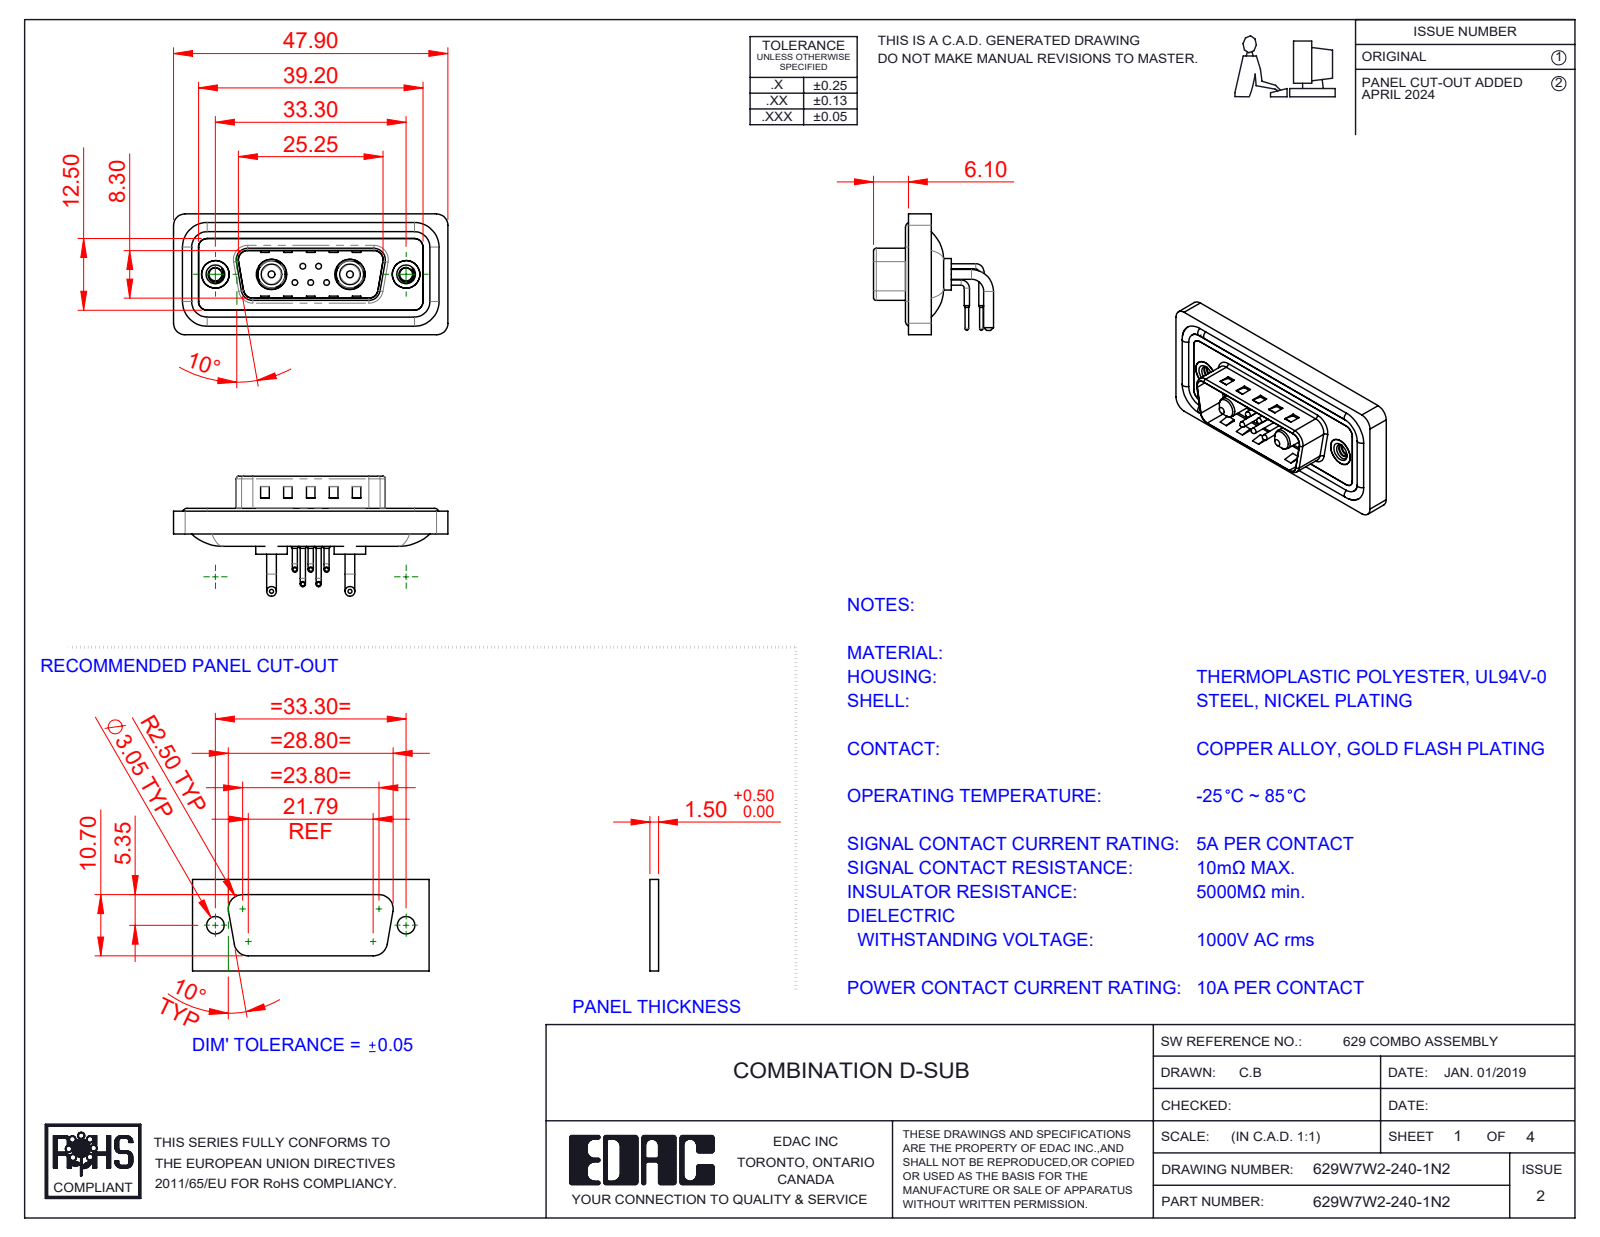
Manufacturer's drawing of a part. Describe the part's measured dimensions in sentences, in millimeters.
The part is named "629Combo Contact Row 1; 629W7W2-140-1N2; 629Combo Housing_7W2; 629Combo Threaded Rivet_2 (+5 more)". Its 3-D file was written by "SolidWorks 2023 (CONFIG_CONTROL_DESIGN)". It is 16 solids with 1083 faces: 517 planar, 406 cylindrical and 160 other. Overall it measures 47.9 by 21.1 by 20.95 millimeters. Its volume is 5 575 cubic millimeters and its surface area 9 039 square millimeters. Round holes: 5 of diameter 0.75, 5 of diameter 1.6, 5 of diameter 2, 2 of diameter 2.26, 2 of diameter 4, 2 of diameter 4.8, 2 of diameter 4.85, 2 of diameter 5, 2 of diameter 5.3. Round bosses or shafts: 10 of diameter 0.9, 5 of diameter 1.5, 5 of diameter 1, 5 of diameter 0.65, 4 of diameter 1.7, 4 of diameter 1.6, 2 of diameter 5.5, 2 of diameter 5.2. Partial cylindrical surfaces (rounded edges, fillets, slot ends): 20 of radius 2, 18 of radius 1.5, 8 of radius 0.5, 8 of radius 1.6, 5 of radius 1.01, 4 of radius 0.25, 4 of radius 0.6, 4 of radius 0.65. The main face-to-face distances are 0.4, 2.9, 0.8, 1.1, 2.1, 1.6, 2.5, 3.1, 4.5, 4.1. The hole center spacings are 3.16, 2.77, 9.8, 23.5, 4.31, 4.33, 5.03, 5.04.
